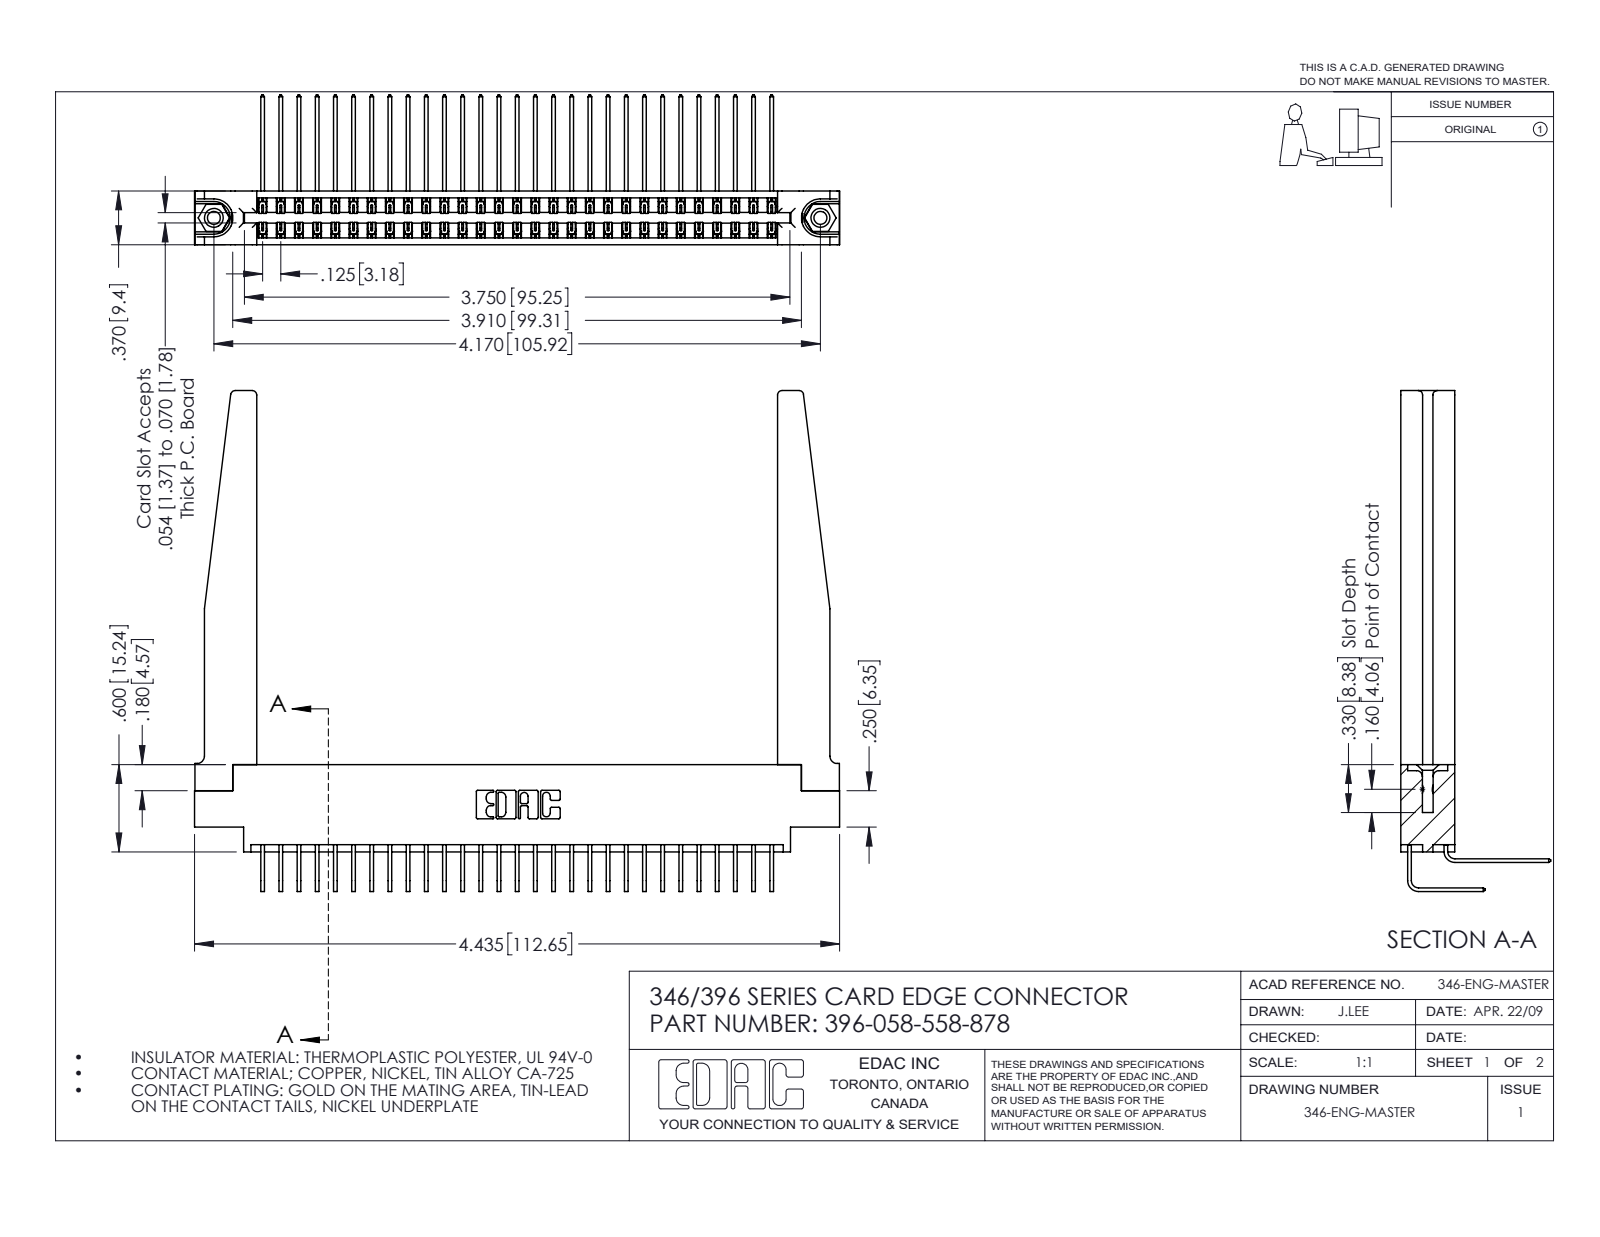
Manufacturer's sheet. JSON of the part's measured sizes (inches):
{"part_name": "345-292-001_558 Tail - 2; 345-250-001_345-250-001-102; 396-058-558-878; 346-220-078_345-220-078 (+2 more)", "step_written_by": "SolidWorks 2016 (CONFIG_CONTROL_DESIGN)", "units": "inches", "bodies": {"solids": 63, "faces": 3492, "planar": 2368, "cylindrical": 1072, "other": 52}, "overall_size": [4.435, 3.443, 1.03], "volume_in3": 1.097, "surface_area_in2": 36.15, "round_holes": [[0.089, 2], [0.125, 2], [0.156, 2], [0.064, 1]], "round_bosses_or_shafts": [[0.155, 2]], "partial_cylinders_radius": [[0.006, 87], [0.01, 22], [0.03, 8], [0.007, 6], [0.031, 6], [0.05, 4], [0.026, 3], [0.014, 2]], "face_to_face_distances": [0.37, 0.322, 0.048, 0.072, 0.025, 0.15, 0.148, 0.25, 0.298, 0.275], "hole_center_spacings": [0.246, 3.962, 4.17]}
